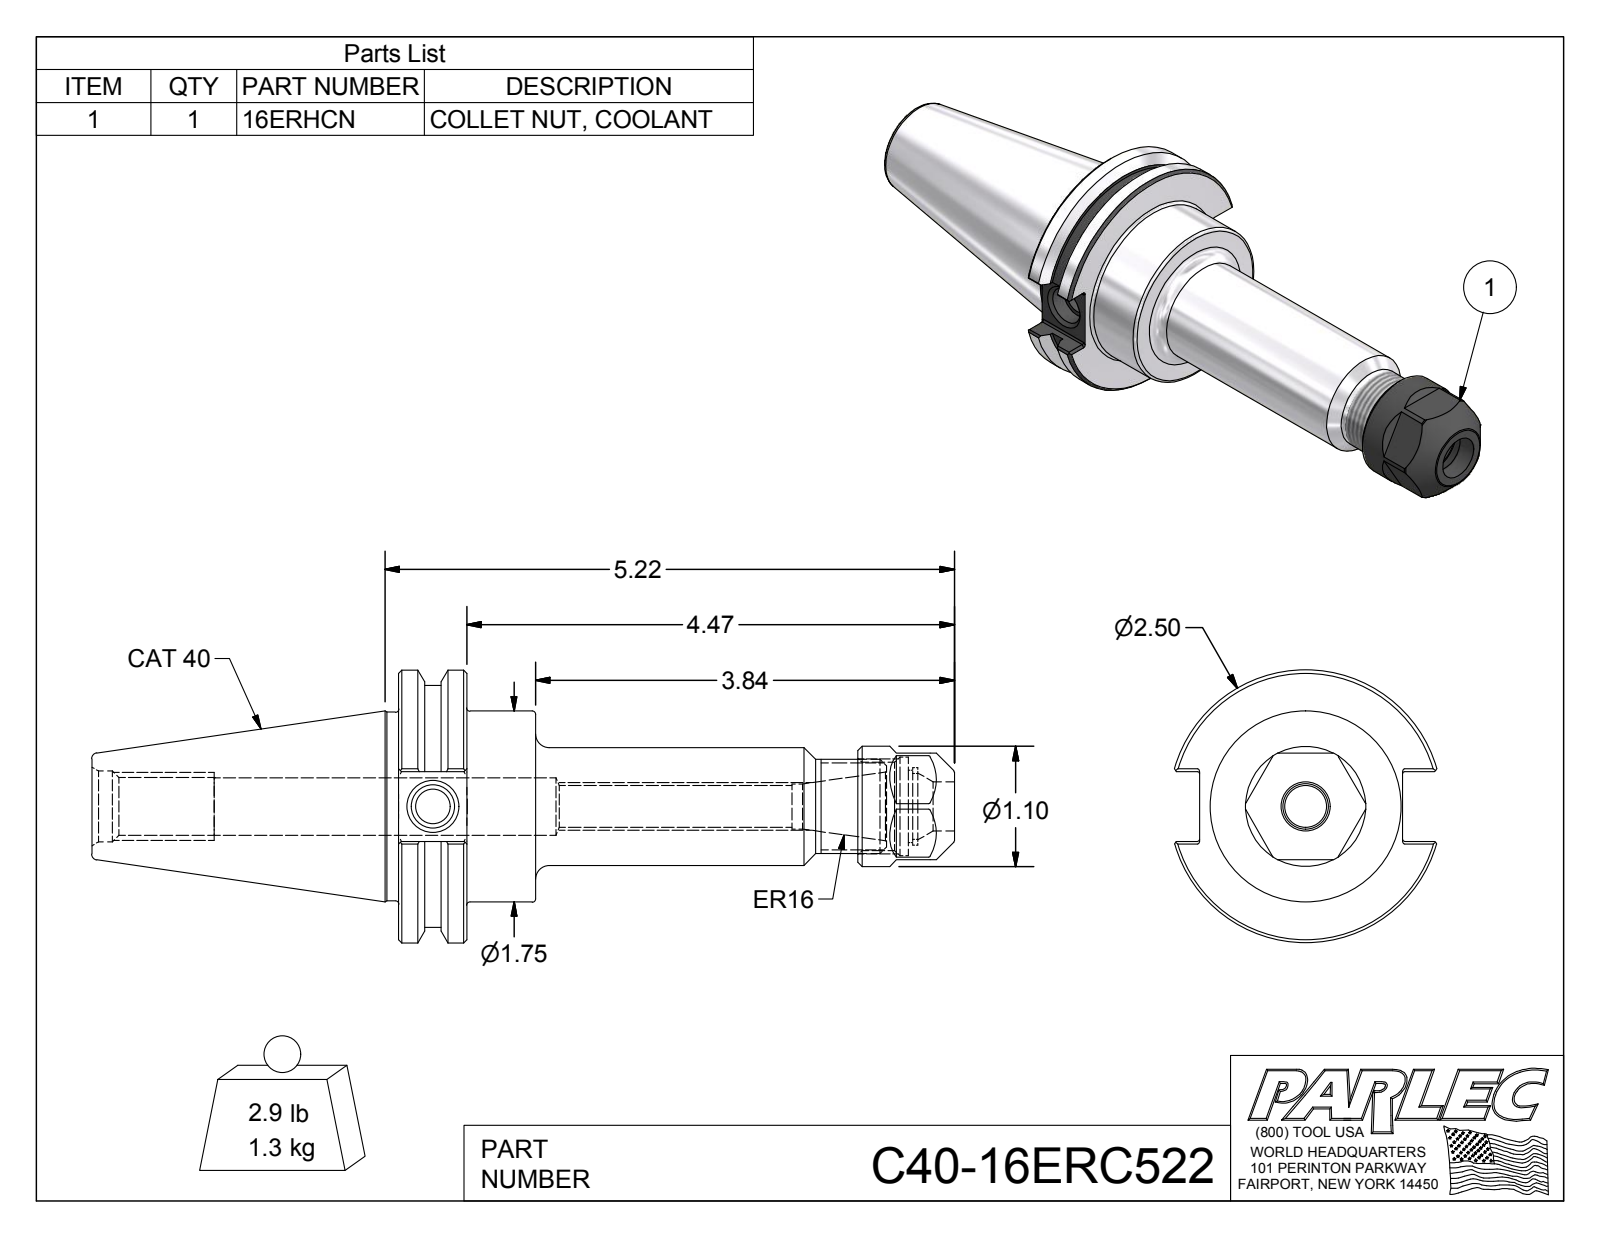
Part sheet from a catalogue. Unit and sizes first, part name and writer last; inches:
Units: inches
Overall size (bounding box): 7.907 × 2.5 × 2.404
Round holes (diameter × count): ⌀0.315 ×1, ⌀0.383 ×1, ⌀0.399 ×1, ⌀0.413 ×1, ⌀0.453 ×1, ⌀0.527 ×1, ⌀0.527 ×1, ⌀0.648 ×1, ⌀0.661 ×1, ⌀0.807 ×1, ⌀0.906 ×1
Round bosses / shafts (diameter × count): ⌀2.5 ×1, ⌀2.219 ×1, ⌀1.75 ×1, ⌀1.73 ×1, ⌀1.102 ×1, ⌀1.08 ×1, ⌀0.866 ×1
Partial cylindrical surfaces — rounded edges, fillets, slot ends (radius × count): R0.02 ×12, R0.354 ×1
Main face-to-face distances: 0.625, 1.255, 0.63, 0.979, 0.169, 0.809, 4.674, 4.049, 3.419, 0.64
Hole centre spacings: 0.051
Volume: 10.13 in³ · Surface area: 56 in²
Bodies: 2 solids, 122 faces (50 planar, 35 cylindrical, 37 other)
Part name (STEP PRODUCT): C40-16ER5-1; 16ERHCN; C40-16ERC522
STEP written by: Autodesk Inventor 2016 (AUTOMOTIVE_DESIGN)
